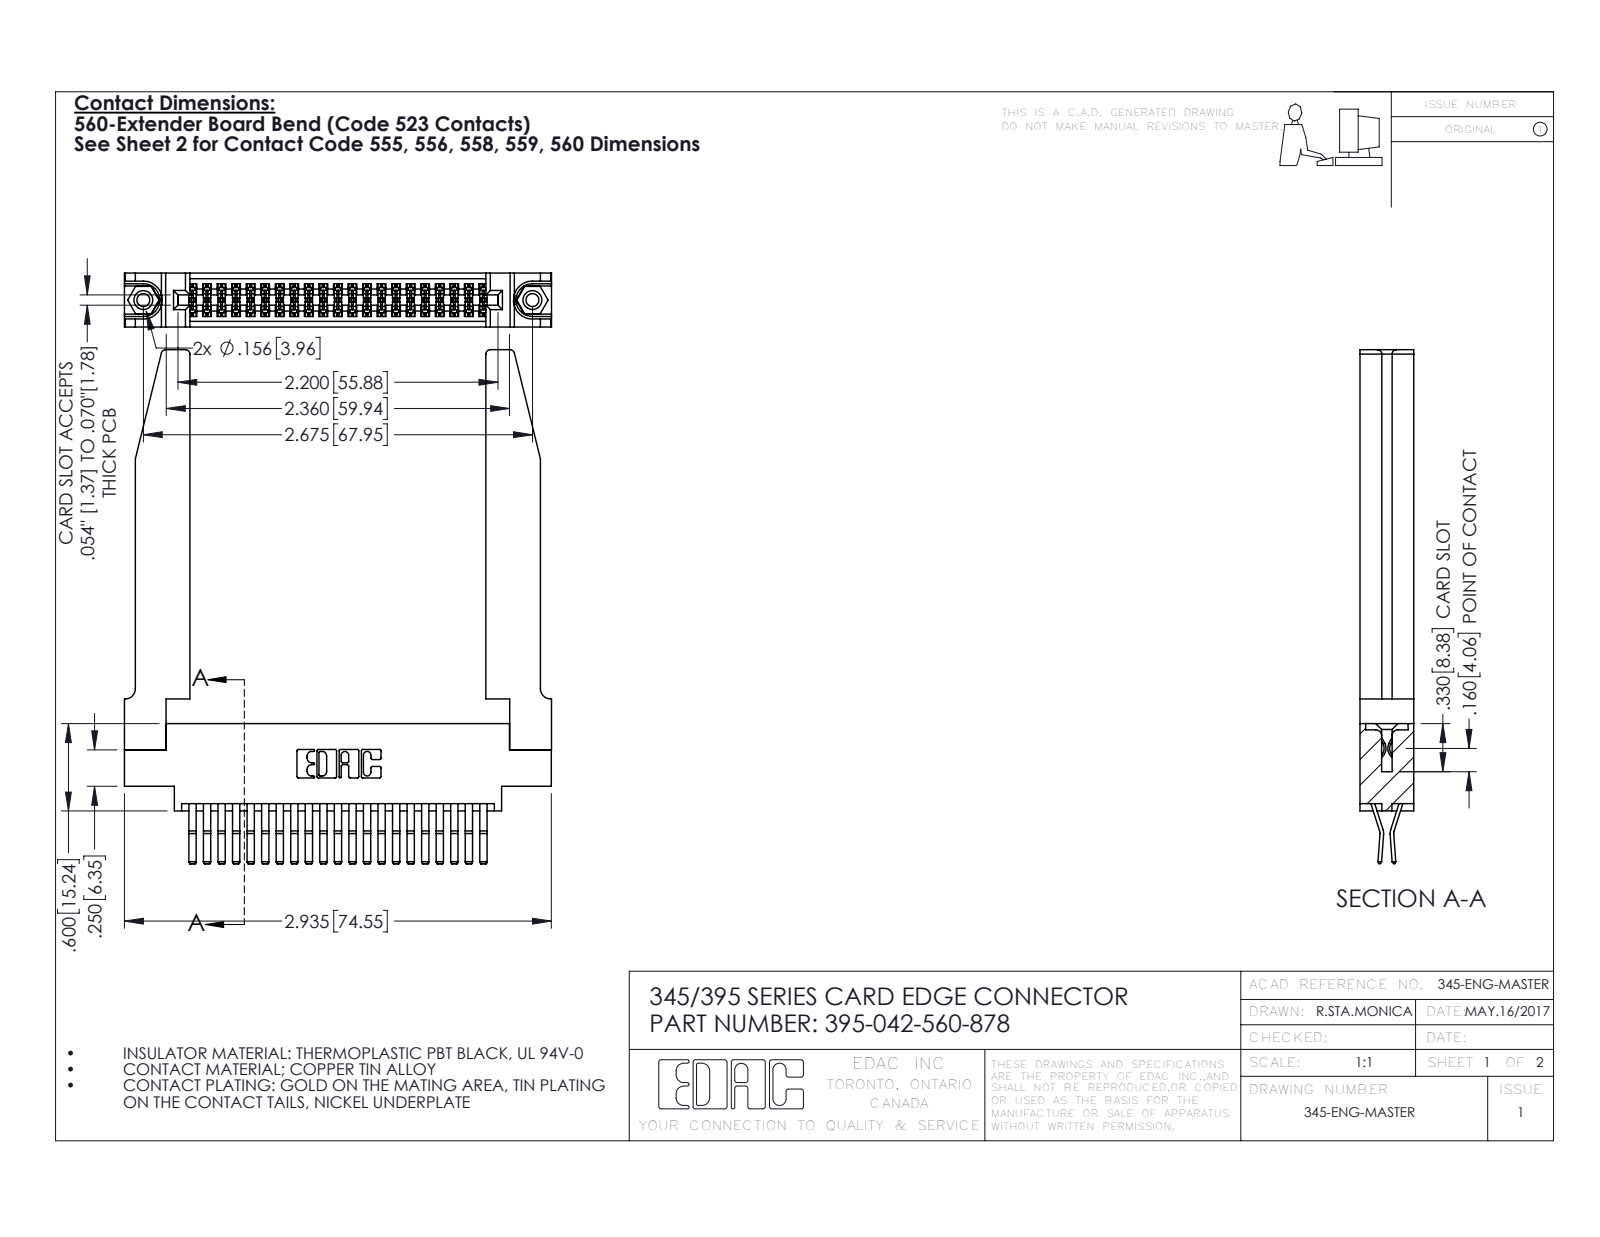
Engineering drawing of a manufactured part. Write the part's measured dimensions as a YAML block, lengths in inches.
part_name: "345-292-001_560 Tail; 345-220-078_345-220-078; 395-042-560-878; 345 Part_0.170 Offset - 0.156 Dia-TH (+1 more)"
step_written_by: "SolidWorks 2016 (CONFIG_CONTROL_DESIGN)"
units: inches
bodies: {solids: 47, faces: 2548, planar: 1612, cylindrical: 884, other: 52}
overall_size: [3.532, 2.936, 0.37]
volume: 0.914
surface_area: 27.81
round_holes:
  - {diameter: 0.089, count: 2}
  - {diameter: 0.125, count: 2}
  - {diameter: 0.156, count: 2}
  - {diameter: 0.064, count: 1}
round_bosses_or_shafts:
  - {diameter: 0.155, count: 2}
partial_cylinders:
  - {radius: 0.006, count: 63}
  - {radius: 0.01, count: 22}
  - {radius: 0.03, count: 8}
  - {radius: 0.007, count: 6}
  - {radius: 0.031, count: 6}
  - {radius: 0.026, count: 3}
  - {radius: 0.01, count: 2}
  - {radius: 0.014, count: 2}
face_to_face_distances: [0.37, 0.072, 0.298, 0.025, 0.098, 0.272, 0.2, 0.225, 0.15, 0.148]
hole_center_spacings: [0.27, 2.441, 2.675]
